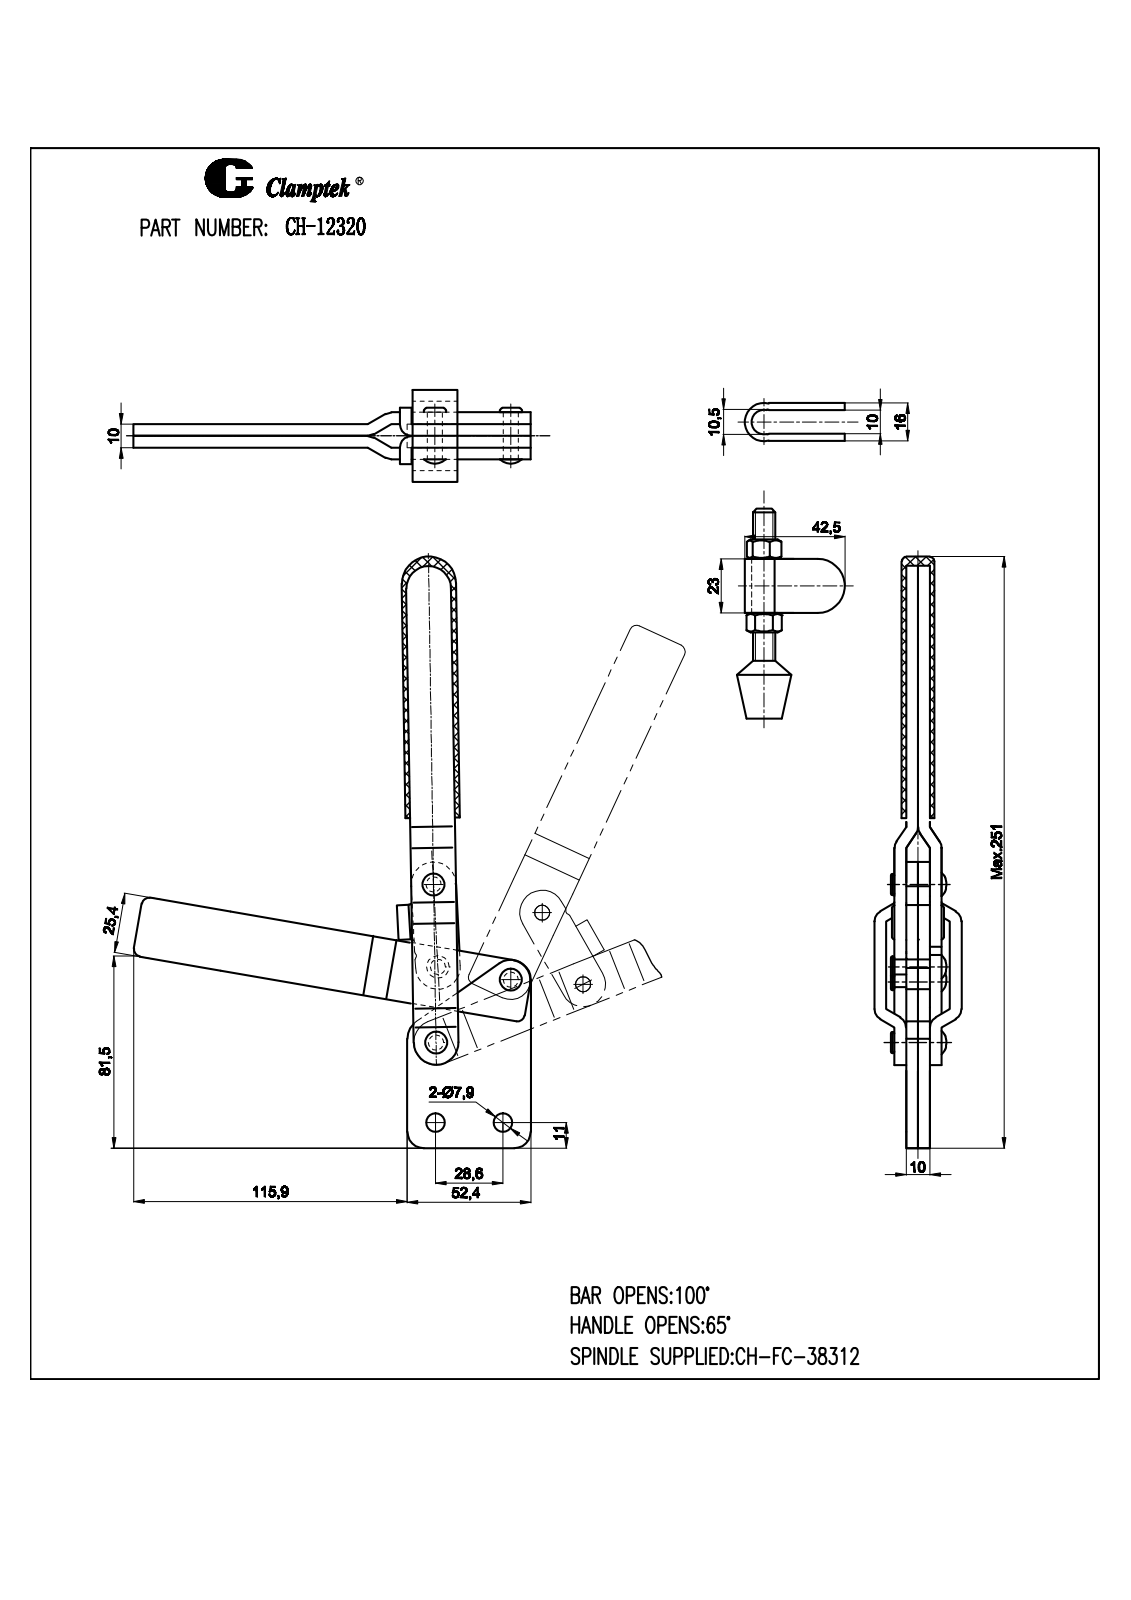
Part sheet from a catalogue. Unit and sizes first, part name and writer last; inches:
Units: inches
Overall size (bounding box): 9.706 × 7.687 × 1.457
Round holes (diameter × count): ⌀0.252 ×4, ⌀0.177 ×2, ⌀0.311 ×2, ⌀0.335 ×2, ⌀0.111 ×1, ⌀0.374 ×1, ⌀0.546 ×1
Round bosses / shafts (diameter × count): ⌀0.374 ×1, ⌀0.109 ×1
Partial cylindrical surfaces — rounded edges, fillets, slot ends (radius × count): R0.197 ×16, R0.039 ×6, R0.118 ×5, R0.079 ×4, R0.374 ×4, R0.197 ×2, R0.276 ×2, R0.335 ×2
Main face-to-face distances: 0.197, 0.394, 0.079, 0.591, 0.118, 0.472, 0.276, 0.669, 0.748, 0.728
Hole centre spacings: 1.126, 1.236, 1.264, 1.332, 1.378, 1.631, 1.737, 2.025
Volume: 9.603 in³ · Surface area: 132.4 in²
Bodies: 11 solids, 829 faces (335 planar, 249 cylindrical, 245 other)
Part name (STEP PRODUCT): 320BR; ѹ; ВЭДё; МЧ (+1 more)
STEP written by: SolidWorks 2015 (CONFIG_CONTROL_DESIGN)
